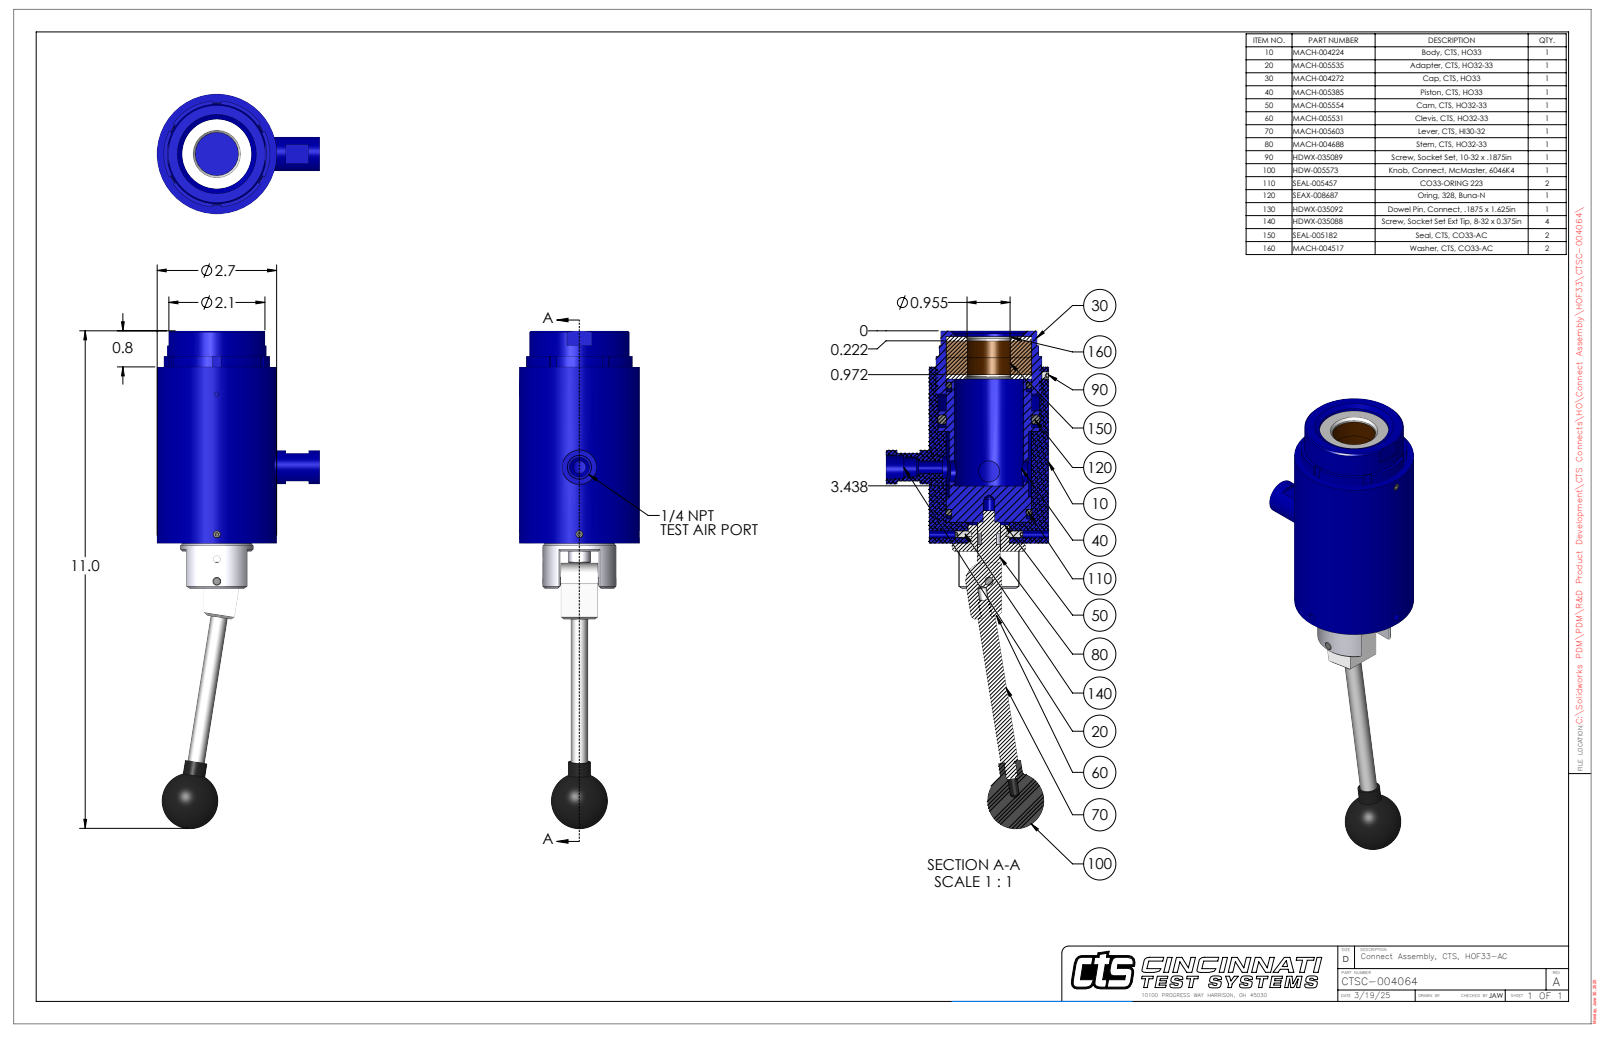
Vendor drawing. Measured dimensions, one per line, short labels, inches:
name: CTSC-004064
written by: SolidWorks 2023 (AUTOMOTIVE_DESIGN)
unit: in
bodies: 14 solids, 546 faces (179 planar, 226 cylindrical, 141 other)
size: 11.035 × 3.6 × 2.65
volume: 22.32 in³; area: 136.6 in²
holes: 3× ⌀0.201, 2× ⌀0.159, 2× ⌀0.469, 1× ⌀0.094, 1× ⌀0.189, 1× ⌀0.19, 1× ⌀0.25, 1× ⌀0.281, 1× ⌀0.438, 1× ⌀0.5, 1× ⌀0.516, 1× ⌀0.524
bosses: 2× ⌀0.75, 2× ⌀0.5, 2× ⌀0.164, 2× ⌀0.109, 1× ⌀2.65, 1× ⌀2.344, 1× ⌀2.2, 1× ⌀1.885
rounds: 1× R0.385, 1× R0.4, 1× R1.13, 1× R1.184
face distances: 0.844, 0.094, 0.75, 0.375, 0.375, 3.736, 4.111, 4.486, 0.469, 3.642
hole spacings: 0.093, 0.488, 1.713, 1.945, 2.033, 2.126, 2.433, 3.658
